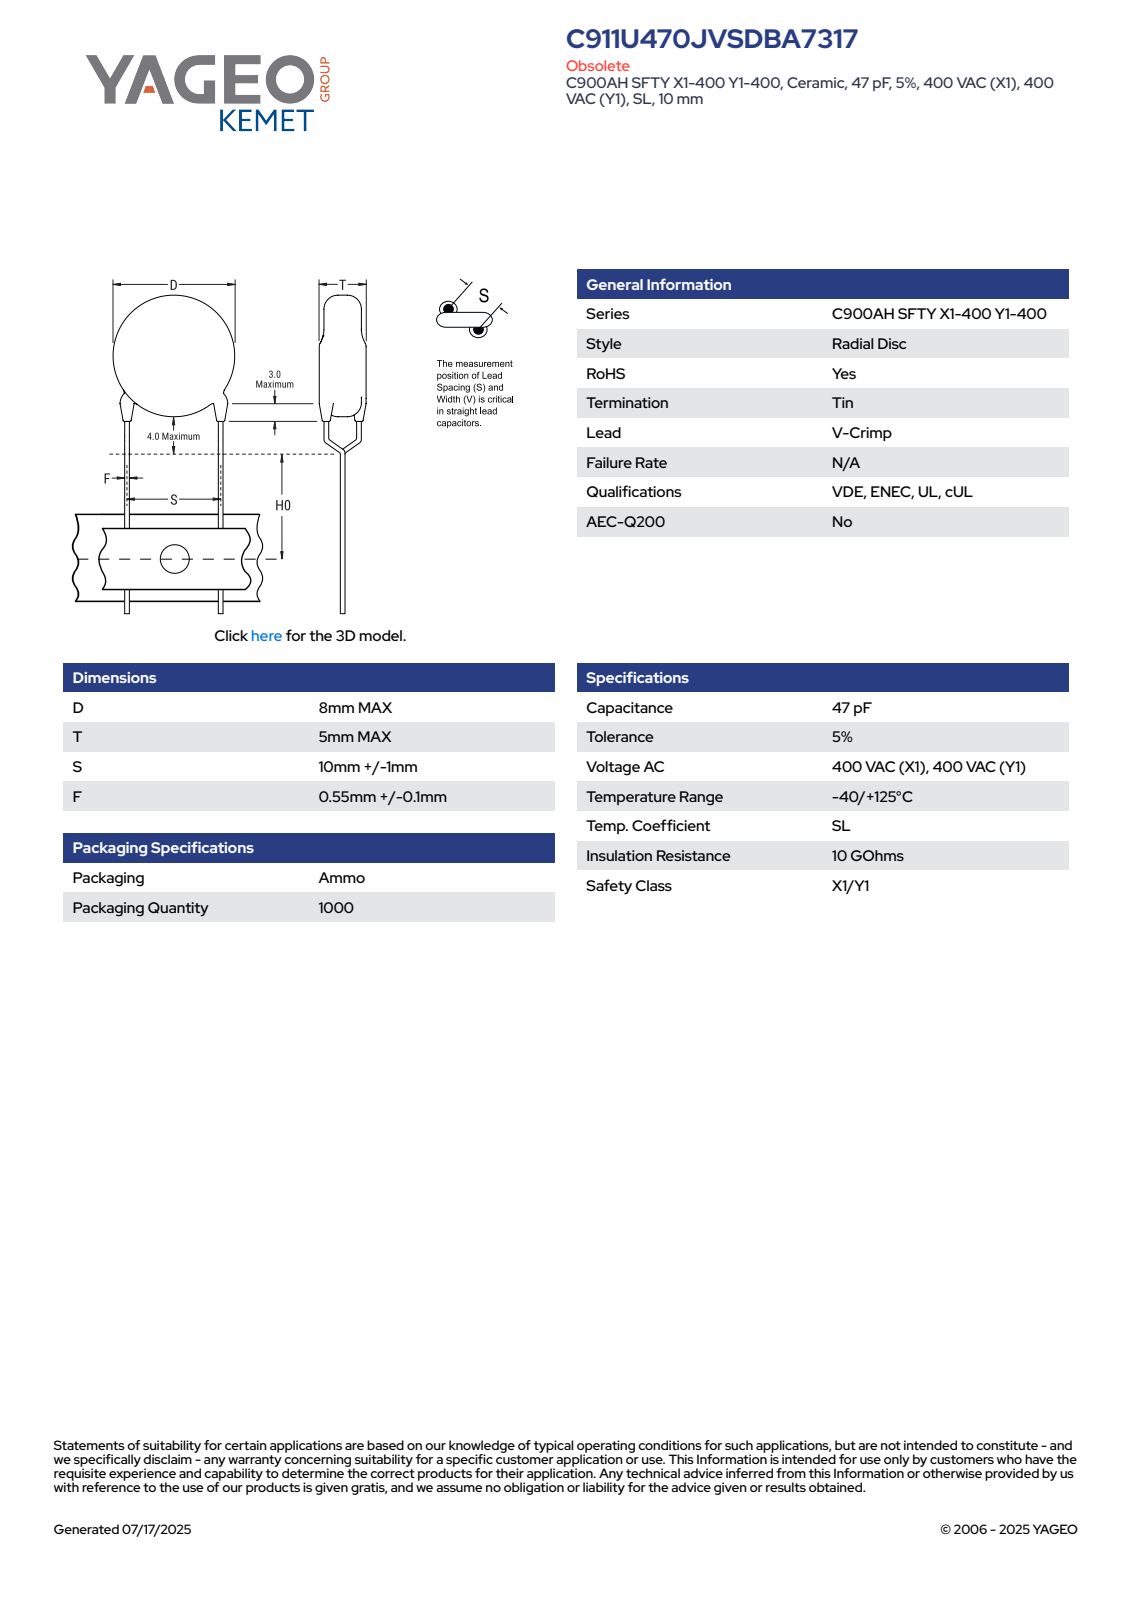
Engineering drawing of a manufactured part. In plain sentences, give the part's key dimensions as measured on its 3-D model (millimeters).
The part is named "CCD_VCC900_D8T5S10LL20F0.65". Its 3-D file was written by "SolidWorks 2014 (AUTOMOTIVE_DESIGN)". It is 5 solids with 93 faces: 65 planar, 16 cylindrical and 12 other. Overall it measures 31.8 by 10.65 by 5 millimeters. Its volume is 262 cubic millimeters and its surface area 325 square millimeters. Round bosses or shafts: 6 of diameter 0.65, 1 of diameter 8. The main face-to-face distances are 5, 22.9, 1.04, 28.32, 5.42, 27.28, 4.38, 0.84, 0.45, 0.39.
